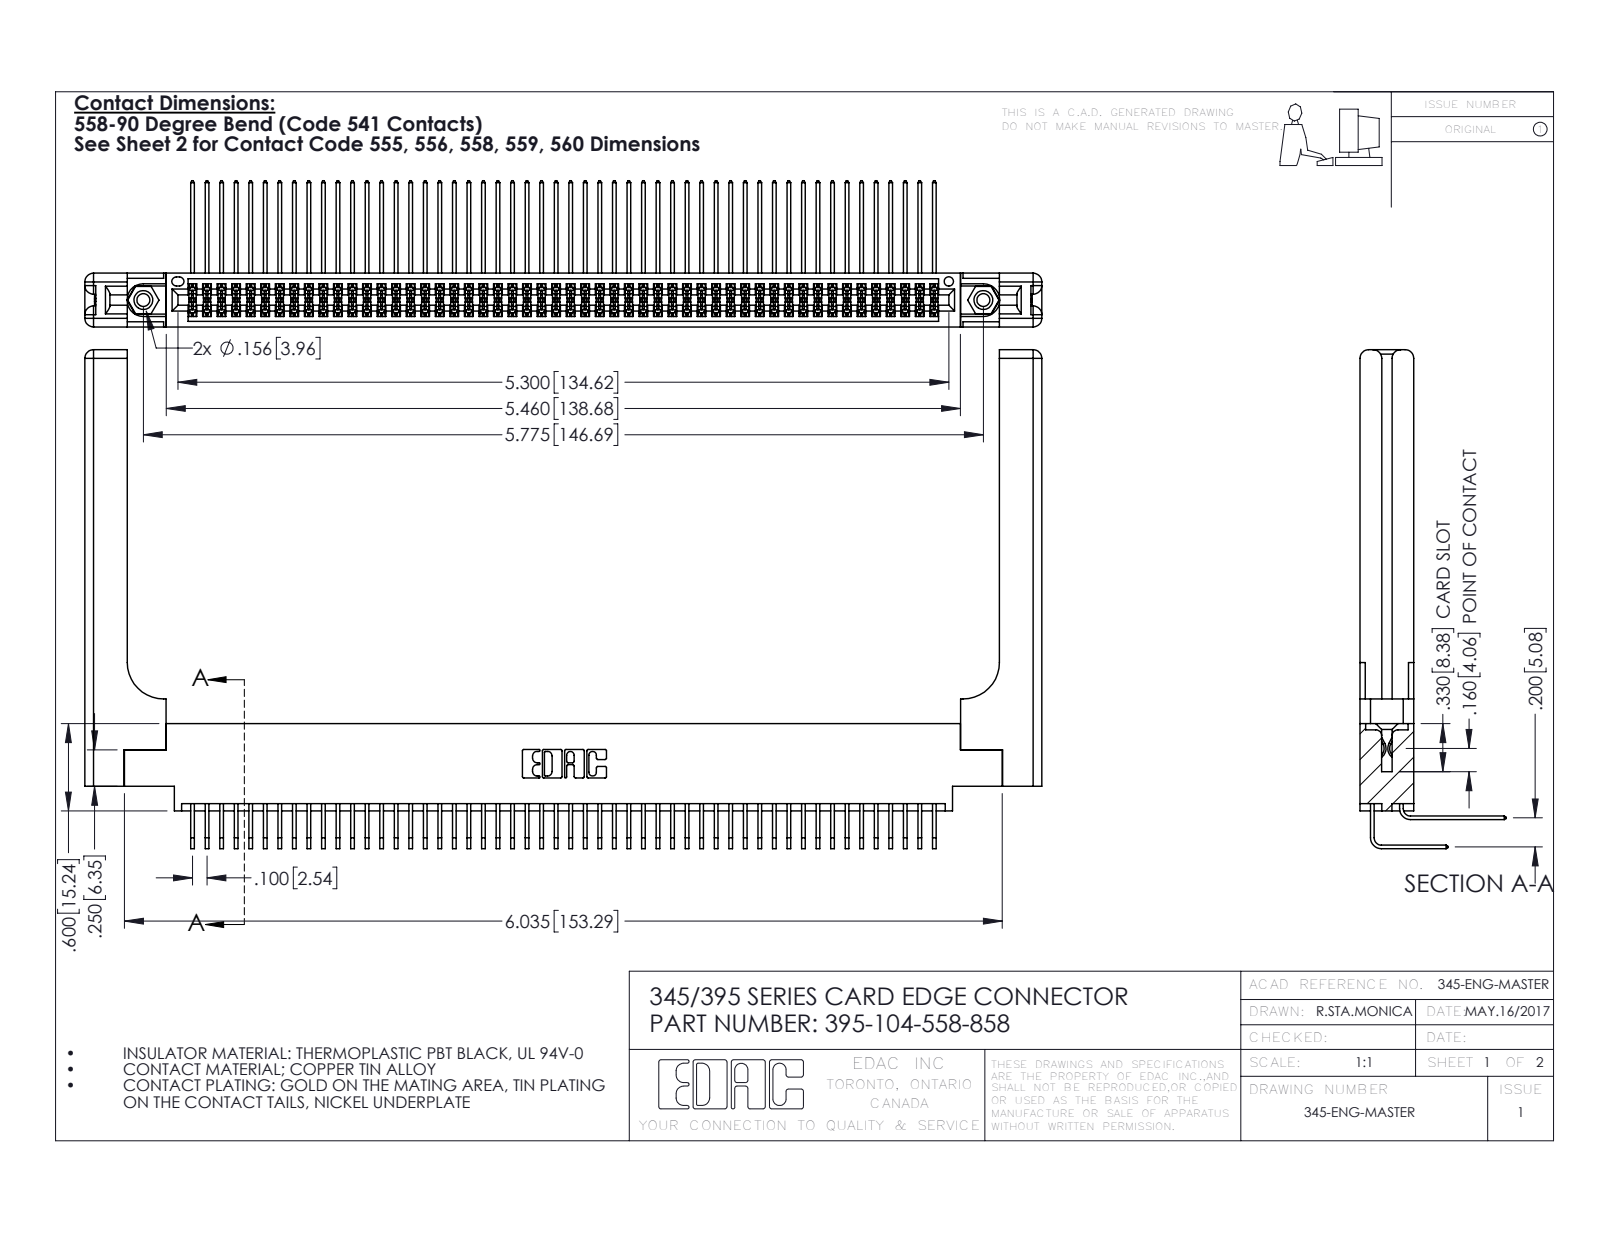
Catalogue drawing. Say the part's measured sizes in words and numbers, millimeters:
The part is named "395-104-558-858; 345 Part_0.170 Offset - 0.156 Dia-TH; 345-250-001_345-250-001-102; 345-220-058_345-220-058 (+2 more)". Its 3-D file was written by "SolidWorks 2016 (CONFIG_CONTROL_DESIGN)". It is 109 solids with 5794 faces: 3872 planar, 1862 cylindrical and 60 other. Overall it measures 167.1 by 87.1 by 25.5 millimeters. Its volume is 25 290 cubic millimeters and its surface area 33 070 square millimeters. Round holes: 2 of diameter 2.3, 2 of diameter 3.2, 2 of diameter 4, 1 of diameter 1.6. Round bosses or shafts: 2 of diameter 3.9. Partial cylindrical surfaces (rounded edges, fillets, slot ends): 157 of radius 0.2, 22 of radius 0.3, 16 of radius 1.5, 6 of radius 0.2, 6 of radius 0.8, 3 of radius 0.7, 2 of radius 0.4, 2 of radius 0.5. The main face-to-face distances are 1.8, 7.6, 9.4, 5.1, 2.5, 6.9, 0.6, 5.7, 4.4, 3.8. The hole center spacings are 6.9, 140.7, 146.7.
